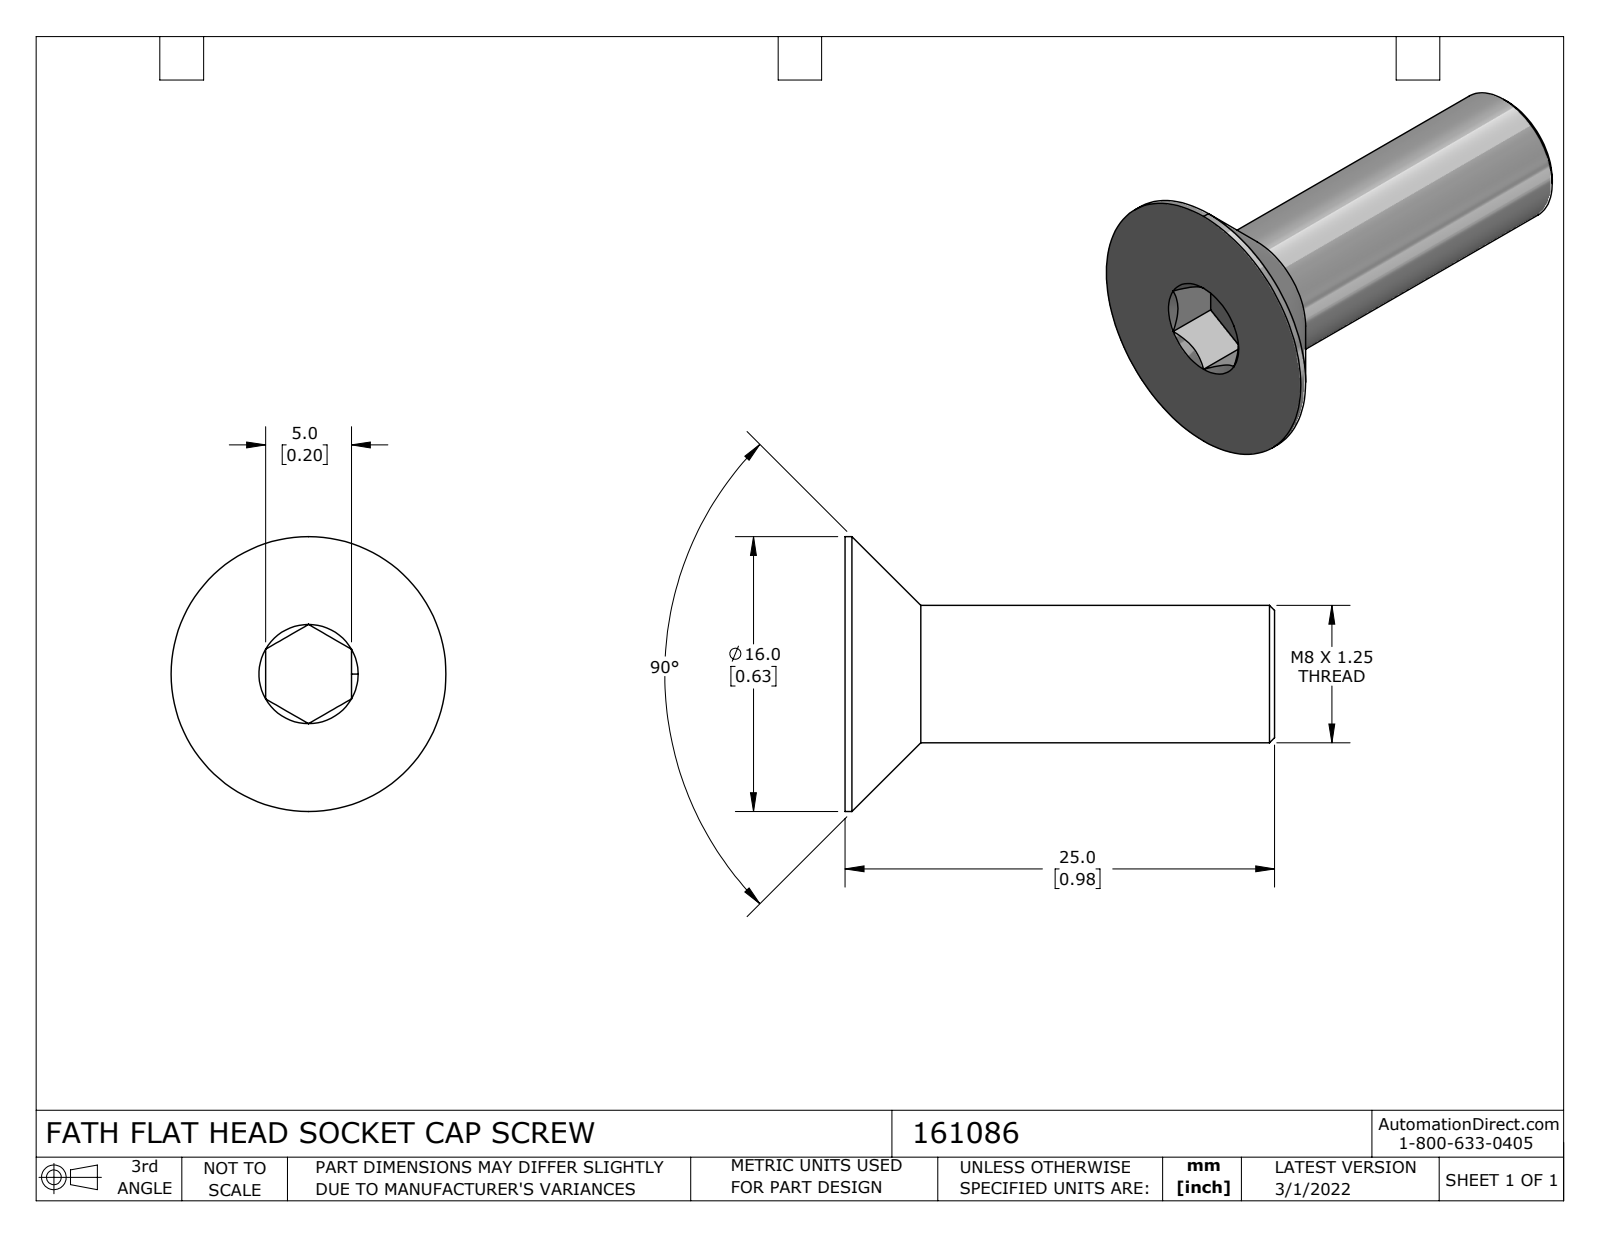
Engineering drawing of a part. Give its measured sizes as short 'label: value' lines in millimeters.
name: 161086
written by: SolidWorks 2021 (CONFIG_CONTROL_DESIGN)
unit: mm
bodies: 1 solid, 24 faces (9 planar, 4 cylindrical, 11 other)
size: 20 × 16 × 16
volume: 1 265 mm³; area: 923 mm²
bosses: 1× ⌀16, 1× ⌀8
face distances: 20, 5, 16.92, 3.08
